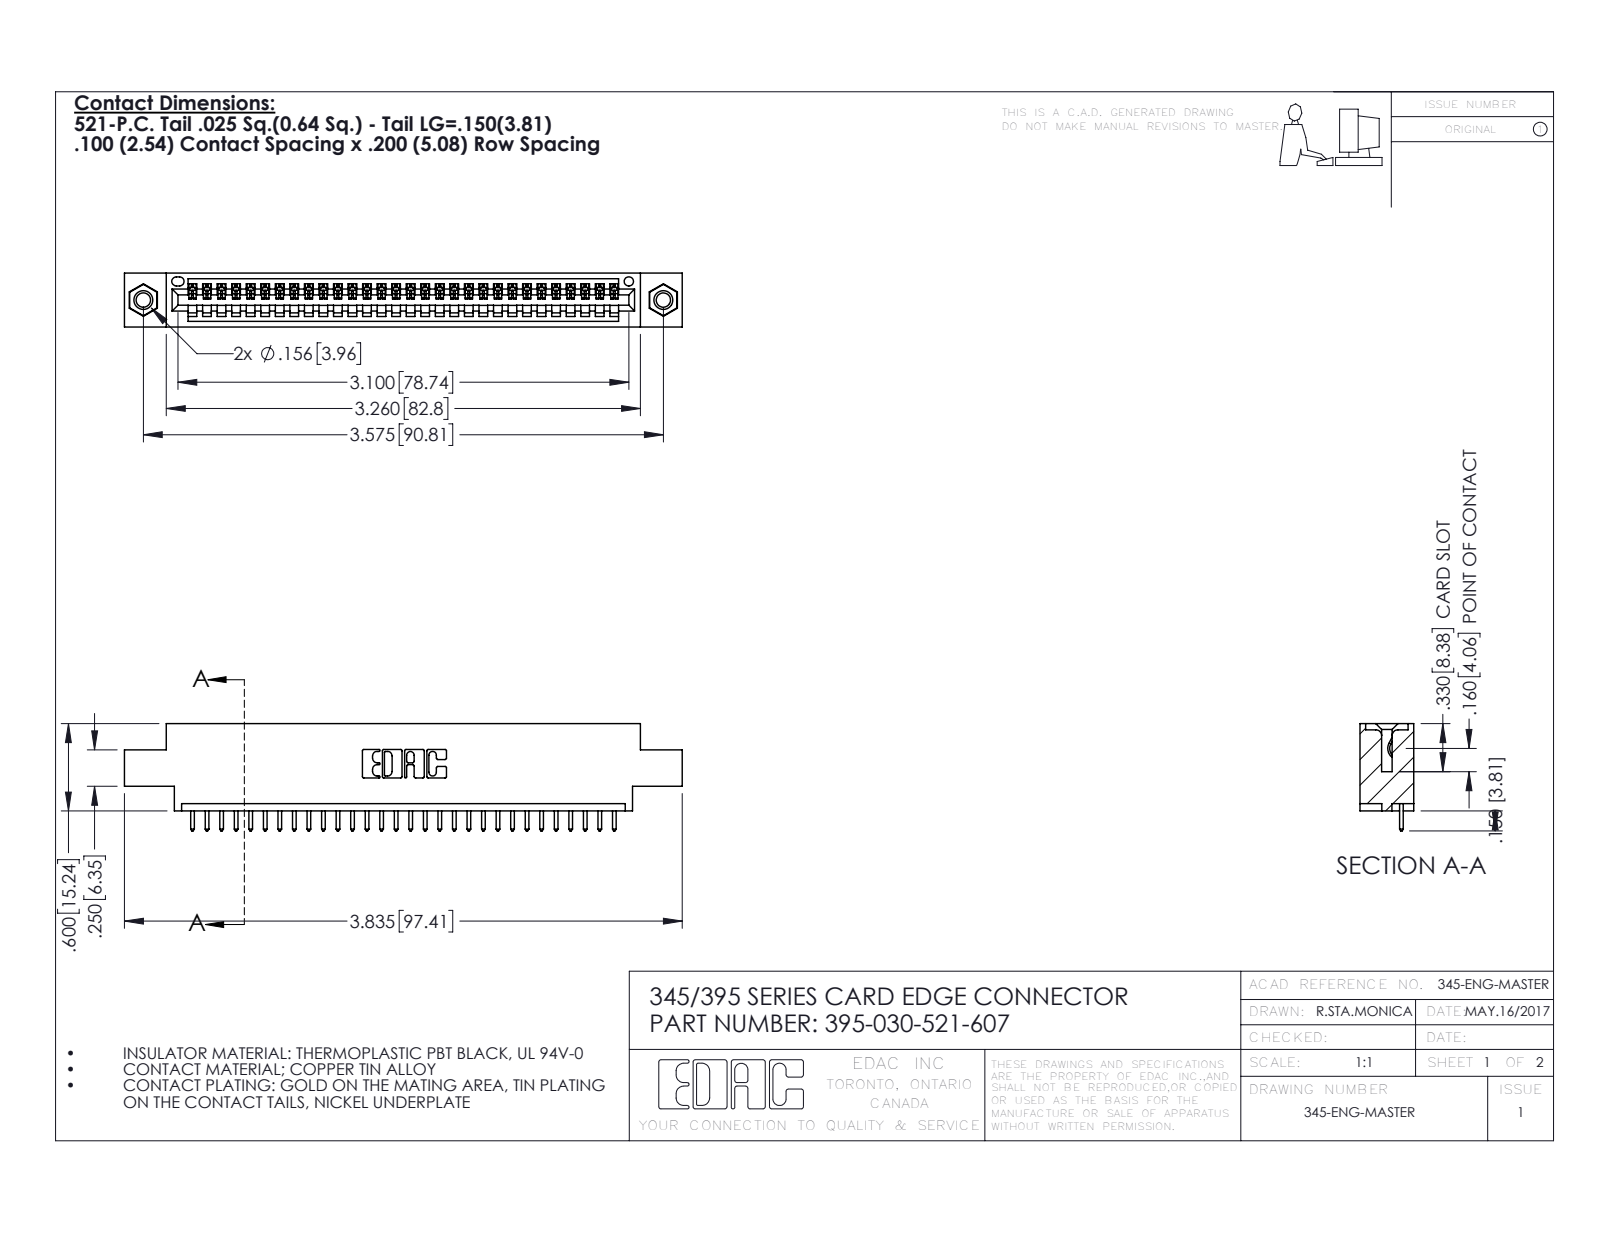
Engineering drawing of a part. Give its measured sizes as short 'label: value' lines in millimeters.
name: 395-030-521-607; 345 Part_0.170 Offset - 0.156 Dia-TI; 345-292-001_345-293-121; 345-250-001_345-250-005-103
written by: SolidWorks 2016 (CONFIG_CONTROL_DESIGN)
unit: mm
bodies: 33 solids, 1930 faces (1316 planar, 598 cylindrical, 16 other)
size: 97.4 × 18.7 × 9.4
volume: 8 950 mm³; area: 11 540 mm²
holes: 2× ⌀2.5, 2× ⌀3.2, 2× ⌀4, 1× ⌀1.6
bosses: 2× ⌀3.9
rounds: 60× R0.2, 60× R0.3, 22× R0.3, 6× R0.2, 6× R0.8, 3× R0.7, 2× R0.8, 2× R1
face distances: 1.8, 7.6, 9.4, 5.1, 2.5, 6.9, 0.6, 5.7, 4.4, 3.8
hole spacings: 6.9, 84.8, 90.8
